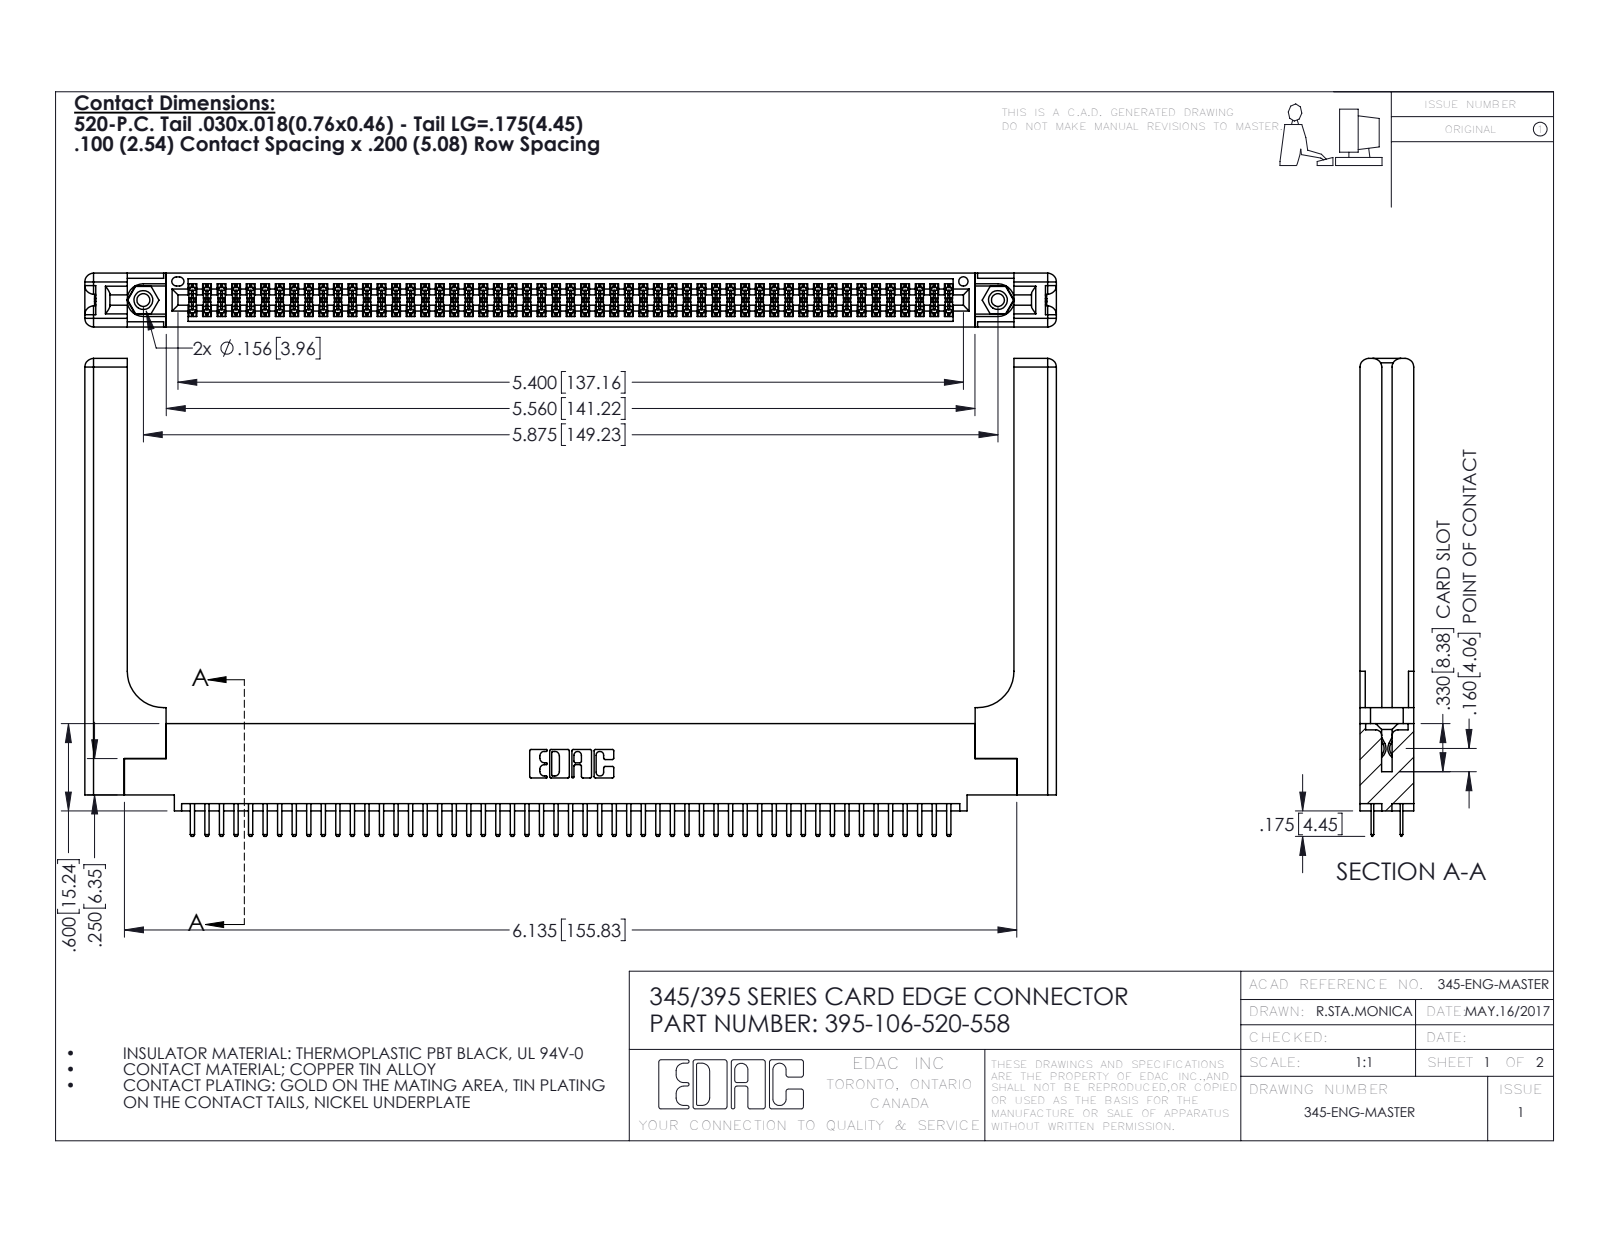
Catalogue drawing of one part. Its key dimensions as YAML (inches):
part_name: "345 Part_0.110 Offset - 0.156 Dia-TH; 395-106-520-558; 345-292-001_345-293-120; 345-220-058_345-220-058 (+1 more)"
step_written_by: "SolidWorks 2016 (CONFIG_CONTROL_DESIGN)"
units: inches
bodies: {solids: 111, faces: 6110, planar: 3942, cylindrical: 2108, other: 60}
overall_size: [6.679, 3.285, 0.37]
volume: 1.522
surface_area: 45.88
round_holes:
  - {diameter: 0.089, count: 2}
  - {diameter: 0.125, count: 2}
  - {diameter: 0.156, count: 2}
  - {diameter: 0.064, count: 1}
round_bosses_or_shafts:
  - {diameter: 0.155, count: 2}
partial_cylinders:
  - {radius: 0.006, count: 159}
  - {radius: 0.01, count: 110}
  - {radius: 0.01, count: 22}
  - {radius: 0.06, count: 16}
  - {radius: 0.007, count: 6}
  - {radius: 0.031, count: 6}
  - {radius: 0.026, count: 3}
  - {radius: 0.014, count: 2}
face_to_face_distances: [0.072, 0.37, 0.298, 0.2, 0.098, 0.272, 0.025, 0.225, 0.148, 0.15]
hole_center_spacings: [0.27, 5.639, 5.875]
